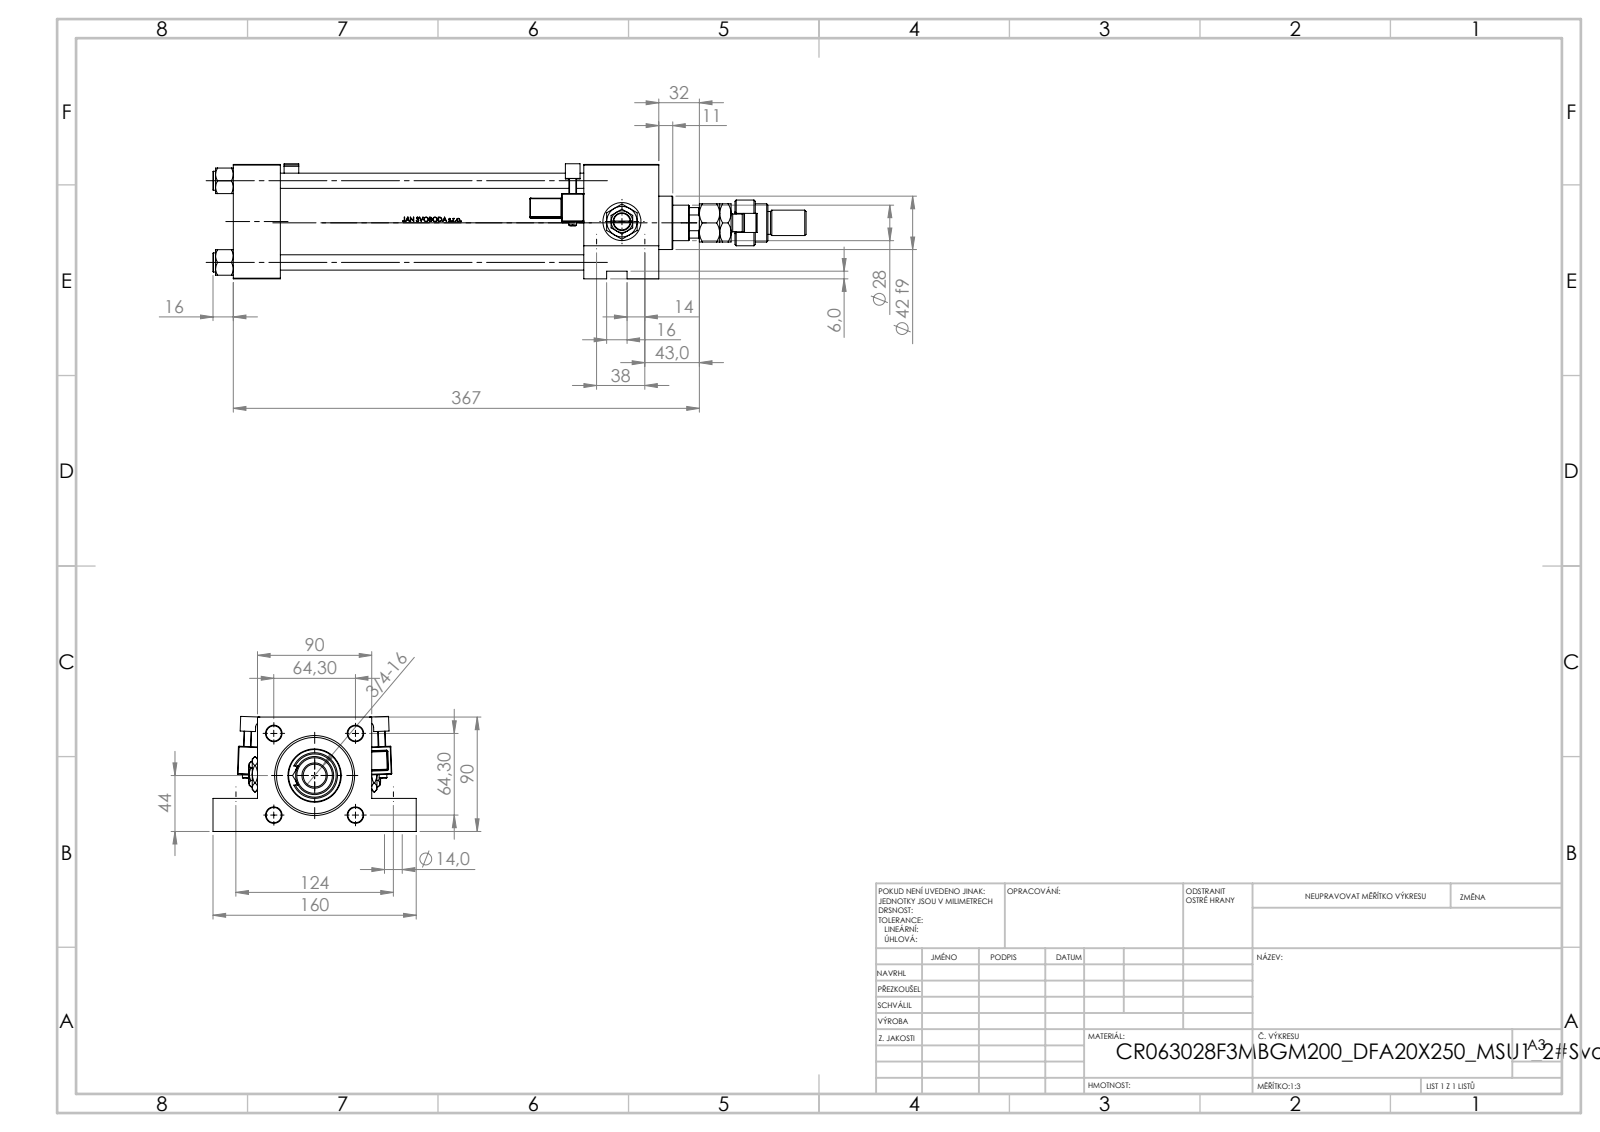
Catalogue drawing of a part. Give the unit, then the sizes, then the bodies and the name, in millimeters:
Units: millimetres
Overall size (bounding box): 467 × 160 × 90.53
Round holes (diameter × count): ⌀12 ×4, ⌀14 ×4, ⌀7 ×2, ⌀30 ×2, ⌀18.5 ×1, ⌀20 ×1, ⌀20.96 ×1, ⌀28 ×1, ⌀31 ×1, ⌀50 ×1, ⌀60 ×1, ⌀63 ×1
Round bosses / shafts (diameter × count): ⌀15 ×4, ⌀6 ×2, ⌀69 ×1, ⌀42 ×1, ⌀36 ×1, ⌀30 ×1, ⌀22 ×1, ⌀20 ×1
Partial cylindrical surfaces — rounded edges, fillets, slot ends (radius × count): R0.5 ×48, R1 ×2, R2.5 ×2, R4 ×2, R7.5 ×1, R12 ×1, R13.5 ×1
Main face-to-face distances: 90, 37, 335, 298, 59, 276, 239, 26, 64, 35
Hole centre spacings: 64.3, 38, 44.77, 46.18, 90.93, 124, 129.69, 287.5
Volume: 1 430 000 mm³ · Surface area: 339 819 mm²
Bodies: 17 solids, 1426 faces (567 planar, 199 cylindrical, 660 other)
Part name (STEP PRODUCT): V215CR_F_TYCINKA; NUT_M5_F; FEMALE_PART_FOR_DFA; V215CR_F_Body (+5 more)
STEP written by: SolidWorks 2019 (CONFIG_CONTROL_DESIGN)
